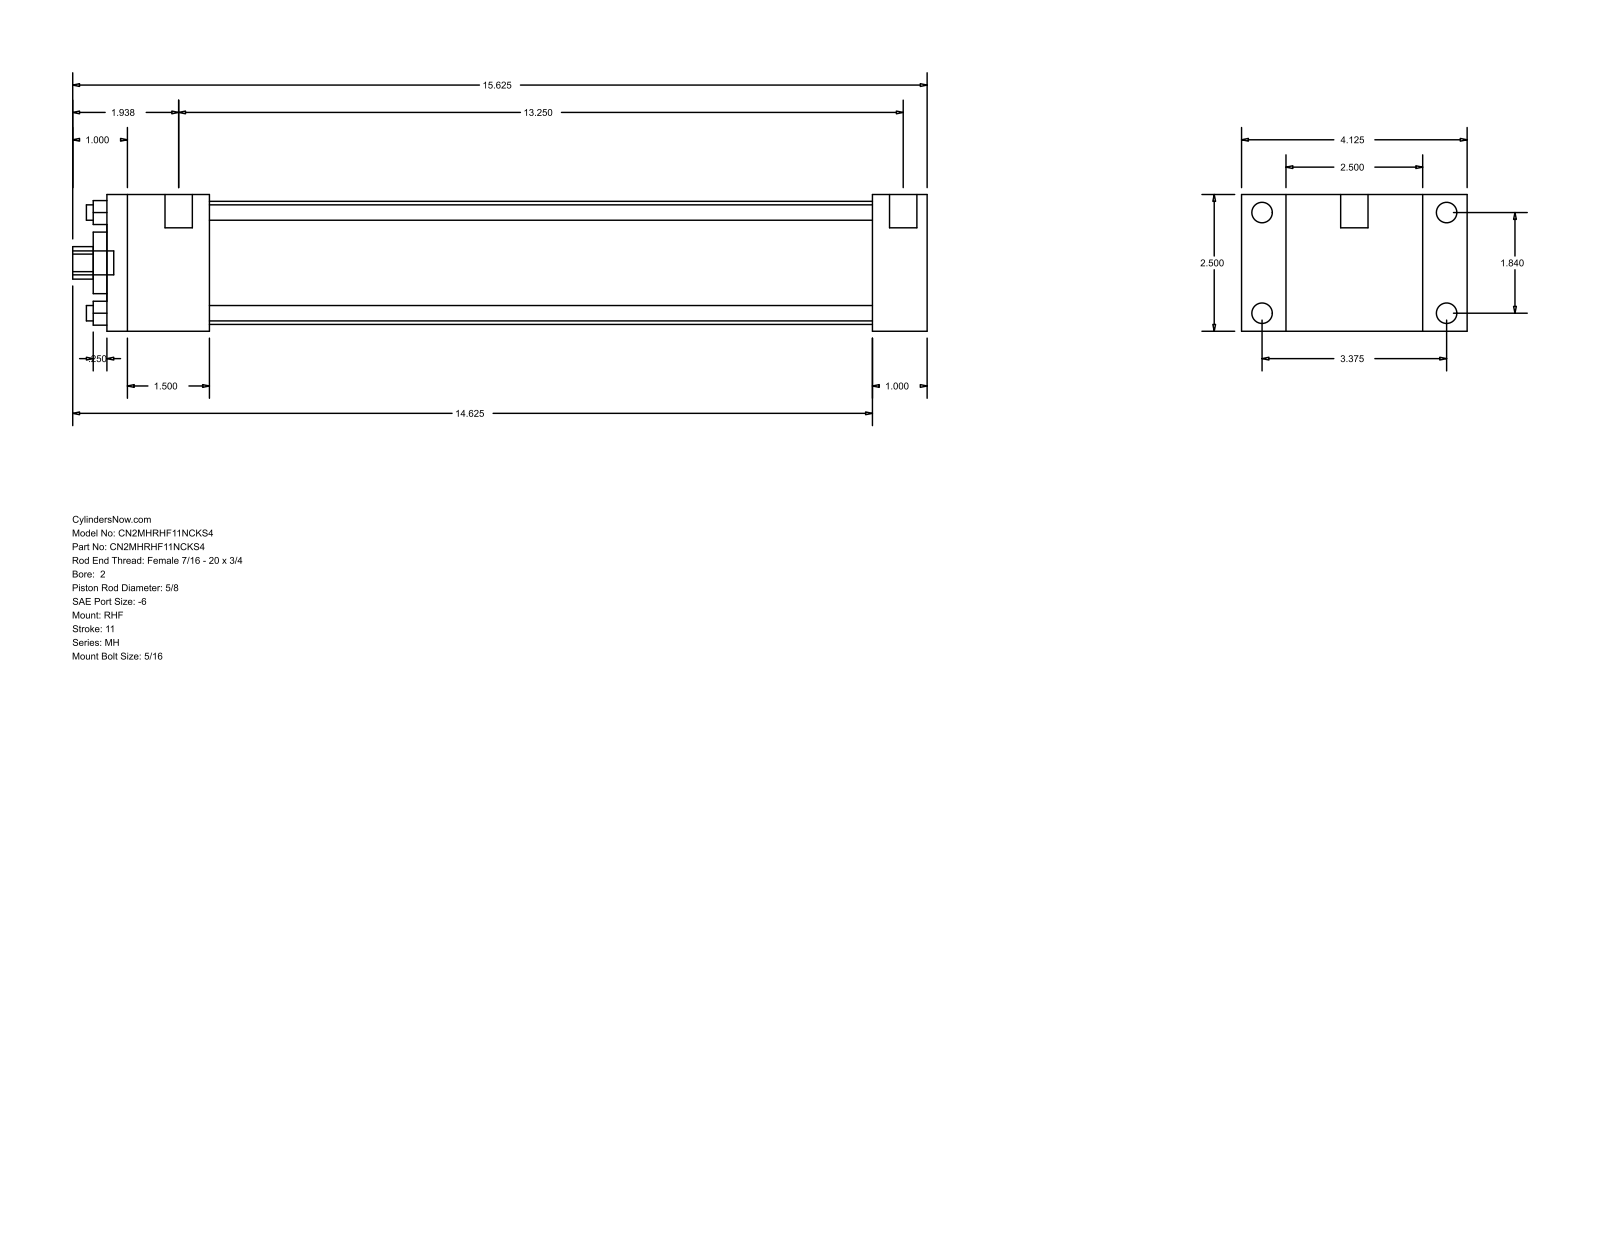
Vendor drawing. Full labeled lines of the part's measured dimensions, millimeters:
Part name (STEP PRODUCT): MH_RHF__0200_0.625
STEP written by: GSSL Pune (CONFIG_CONTROL_DESIGN)
Units: millimetres
Bodies: 0 solids, 88 faces (60 planar, 28 cylindrical, 0 other)
Overall size (bounding box): 396.88 × 104.78 × 63.5
Round holes (diameter × count): ⌀7.14 ×4, ⌀15.88 ×1, ⌀28.57 ×1, ⌀57.15 ×1
Round bosses / shafts (diameter × count): ⌀9.53 ×4, ⌀5.56 ×4, ⌀12.7 ×2, ⌀11.11 ×1
Partial cylindrical surfaces — rounded edges, fillets, slot ends (radius × count): R7.54 ×1
Main face-to-face distances: 63.5, 25.4, 20.64, 84.14, 355.6, 381, 104.78, 47.62, 307.98, 333.38
Hole centre spacings: 33.05, 46.74, 66.1
